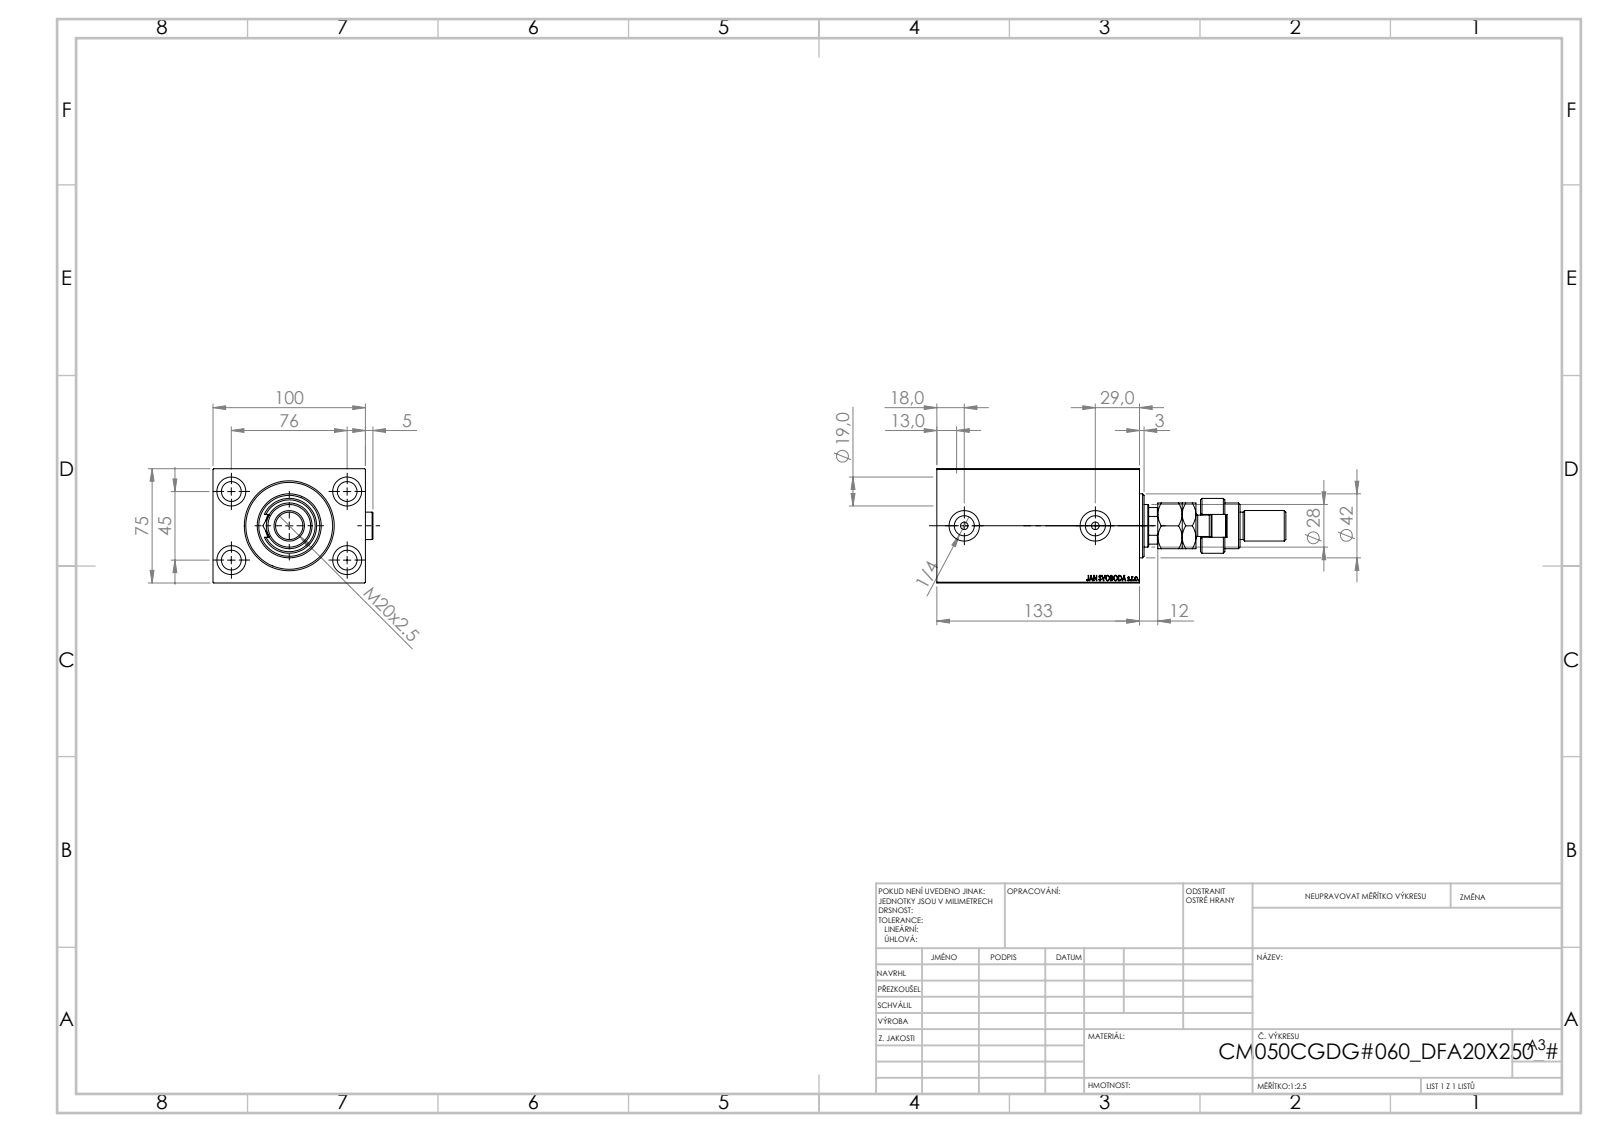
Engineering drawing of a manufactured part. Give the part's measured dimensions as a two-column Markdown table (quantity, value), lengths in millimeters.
| quantity | value |
| --- | --- |
| part name | MFA; V450CM_C_Body; Zatka_OIL_PORT; V450CM_VC_B (+2 more) |
| STEP written by | SolidWorks 2019 (CONFIG_CONTROL_DESIGN) |
| units | millimeters |
| bodies | 7 solids, 1004 faces (471 planar, 91 cylindrical, 442 other) |
| overall size | 229 × 104.9 × 75 |
| volume | 874 862 mm³ |
| surface area | 148 278 mm² |
| round holes (diameter × count) | 13 × 4, 19 × 4, 5 × 2, 13.16 × 2, 20 × 2, 18.5 × 1, 28 × 1, 31.5 × 1, 50 × 1, 52 × 1, 57 × 1 |
| round bosses / shafts (diameter × count) | 18 × 3, 42 × 1, 36 × 1, 30 × 1, 22 × 1, 20 × 1, 14 × 1 |
| partial cylindrical surfaces (radius × count) | 7.5 × 1, 12 × 1, 13.5 × 1 |
| main face-to-face distances | 75, 100, 133, 119, 14, 12, 107, 30, 60, 121 |
| hole center spacings | 44.16, 45, 76, 88.32, 86 |
